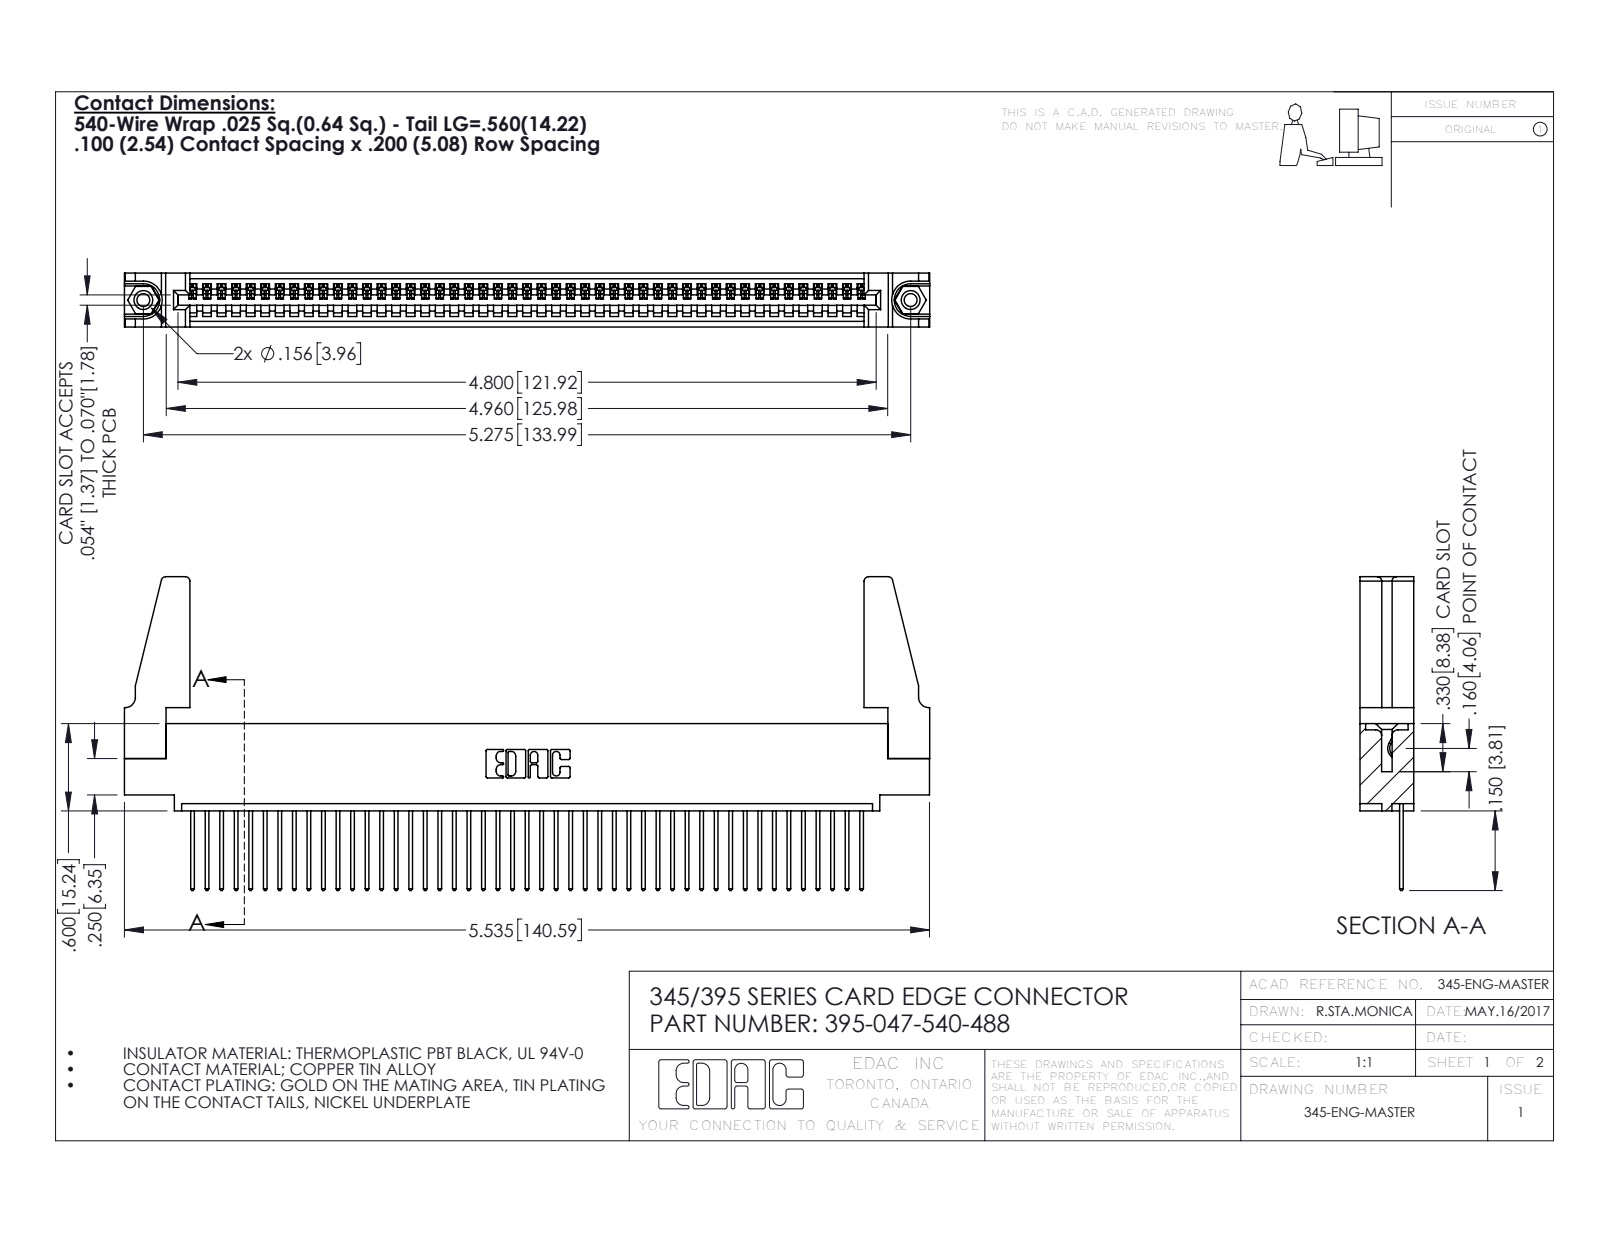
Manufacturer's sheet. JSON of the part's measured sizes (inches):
{"part_name": "395-047-540-488; 345-292-001_345-293-140; 345-250-001_345-250-001-102; 345 Part_0.110 Offset - 0.156 Dia-TH (+1 more)", "step_written_by": "SolidWorks 2016 (CONFIG_CONTROL_DESIGN)", "units": "inches", "bodies": {"solids": 52, "faces": 2980, "planar": 2036, "cylindrical": 928, "other": 16}, "overall_size": [5.536, 2.157, 0.37], "volume_in3": 1.015, "surface_area_in2": 33.37, "round_holes": [[0.089, 2], [0.125, 2], [0.156, 2], [0.064, 1]], "round_bosses_or_shafts": [[0.155, 2]], "partial_cylinders_radius": [[0.006, 94], [0.01, 94], [0.01, 22], [0.03, 8], [0.007, 6], [0.031, 6], [0.026, 3], [0.031, 2]], "face_to_face_distances": [0.072, 0.298, 0.37, 0.098, 0.272, 0.025, 0.2, 0.225, 0.149, 0.072], "hole_center_spacings": [0.27, 5.039, 5.275]}
